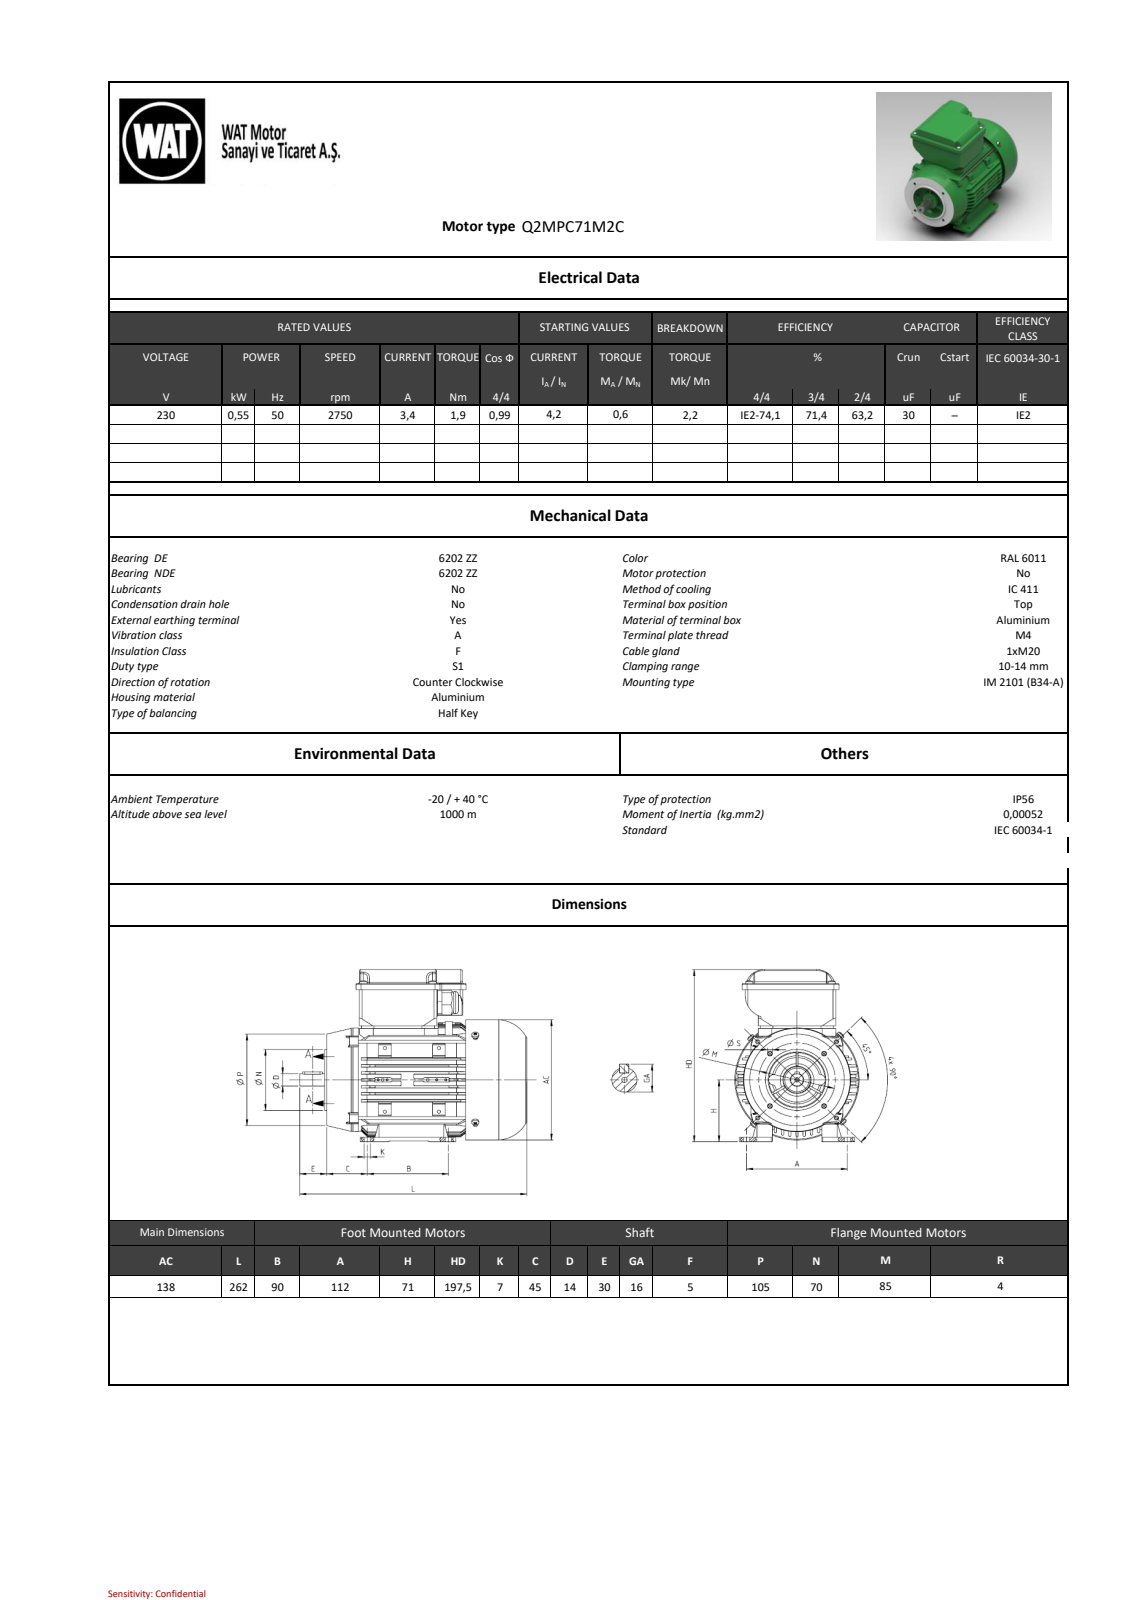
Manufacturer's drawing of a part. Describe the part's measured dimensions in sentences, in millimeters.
The part is named "BY6434017xx_004-TK_QM63-80; BY6424130xx_004-TKK_QM63-80; BY6432003xx_006-MOTOR_KAPAGI_QS71_FC_ISLEME; 641304741_AZ-KAMA PARALEL A 5x5x22 St50 DIN6885 (+8 more)". Its 3-D file was written by "SIEMENS PLM Software NX2206.8101 (AUTOMOTIVE_DESIGN)". It is 26 solids with 2797 faces: 1337 planar, 801 cylindrical and 659 other. Overall it measures 262 by 197.5 by 138 millimeters. Its volume is 795 723 cubic millimeters and its surface area 502 403 square millimeters. Round holes: 8 of diameter 3.65, 8 of diameter 4.5, 7 of diameter 3, 6 of diameter 2.5, 5 of diameter 3.3, 4 of diameter 4, 4 of diameter 4.65, 4 of diameter 4.8, 4 of diameter 5.2, 4 of diameter 7, 3 of diameter 3.7, 2 of diameter 4.6. Round bosses or shafts: 8 of diameter 8, 8 of diameter 4, 8 of diameter 3, 4 of diameter 12, 4 of diameter 3.3, 1 of diameter 138, 1 of diameter 70, 1 of diameter 26. Partial cylindrical surfaces (rounded edges, fillets, slot ends): 165 of radius 1, 53 of radius 2, 41 of radius 0.5, 36 of radius 1.2, 20 of radius 5, 16 of radius 3.25, 16 of radius 10, 14 of radius 2.5. The main face-to-face distances are 3, 194.5, 4, 36, 5, 197.5, 1, 158.5, 19, 32. The hole center spacings are 87.43, 55, 36.59, 60, 28.5, 37.26, 61.77, 61.87.
